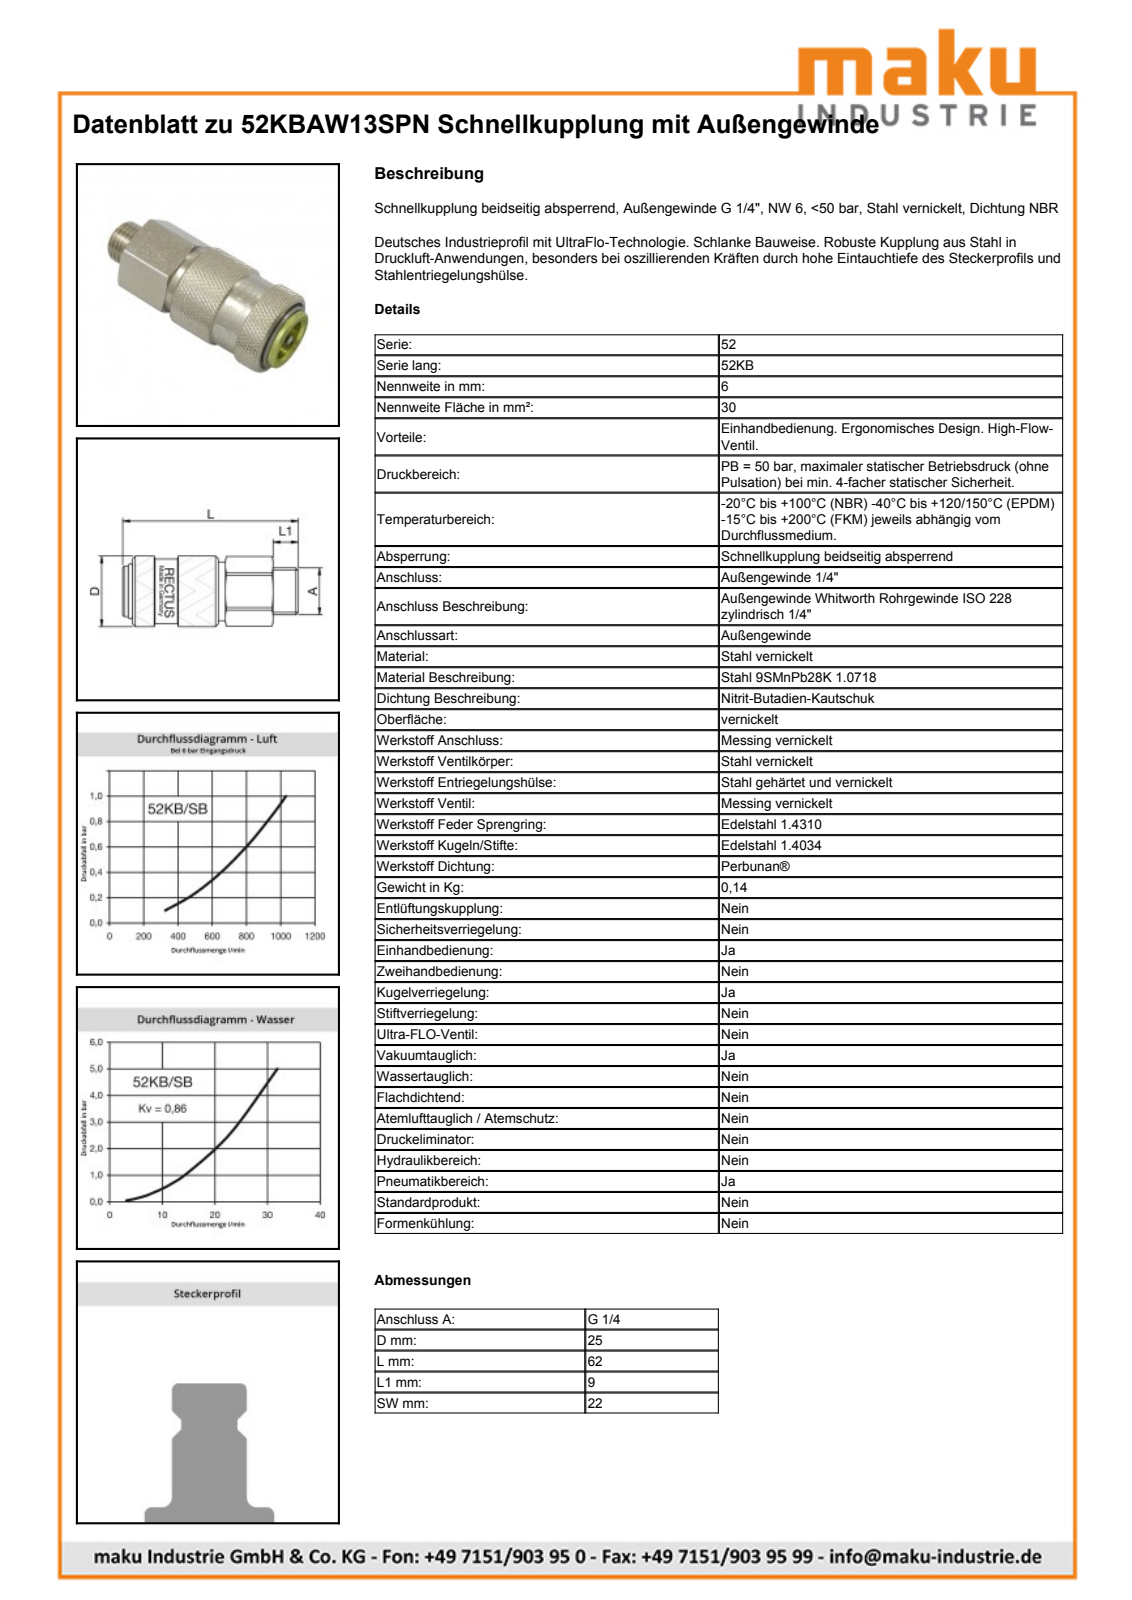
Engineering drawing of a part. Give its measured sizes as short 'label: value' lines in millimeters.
name: D106282
written by: Autodesk Inventor 2011 (AUTOMOTIVE_DESIGN)
unit: mm
bodies: 3 solids, 517 faces (196 planar, 64 cylindrical, 257 other)
size: 62.55 × 25.15 × 25.15
volume: 22 848 mm³; area: 11 887 mm²
holes: 1× ⌀14, 1× ⌀14.1, 1× ⌀15.35, 1× ⌀17, 1× ⌀18.25, 1× ⌀20.5, 1× ⌀21
bosses: 1× ⌀25.15, 1× ⌀23, 1× ⌀20.85, 1× ⌀18, 1× ⌀16.65, 1× ⌀16.5, 1× ⌀13.94, 1× ⌀13.16
rounds: 1× R11.4, 1× R12.4
face distances: 22, 53.55, 3.5, 3.32, 9, 62.55, 55.73, 46.73, 6.82, 40.23
